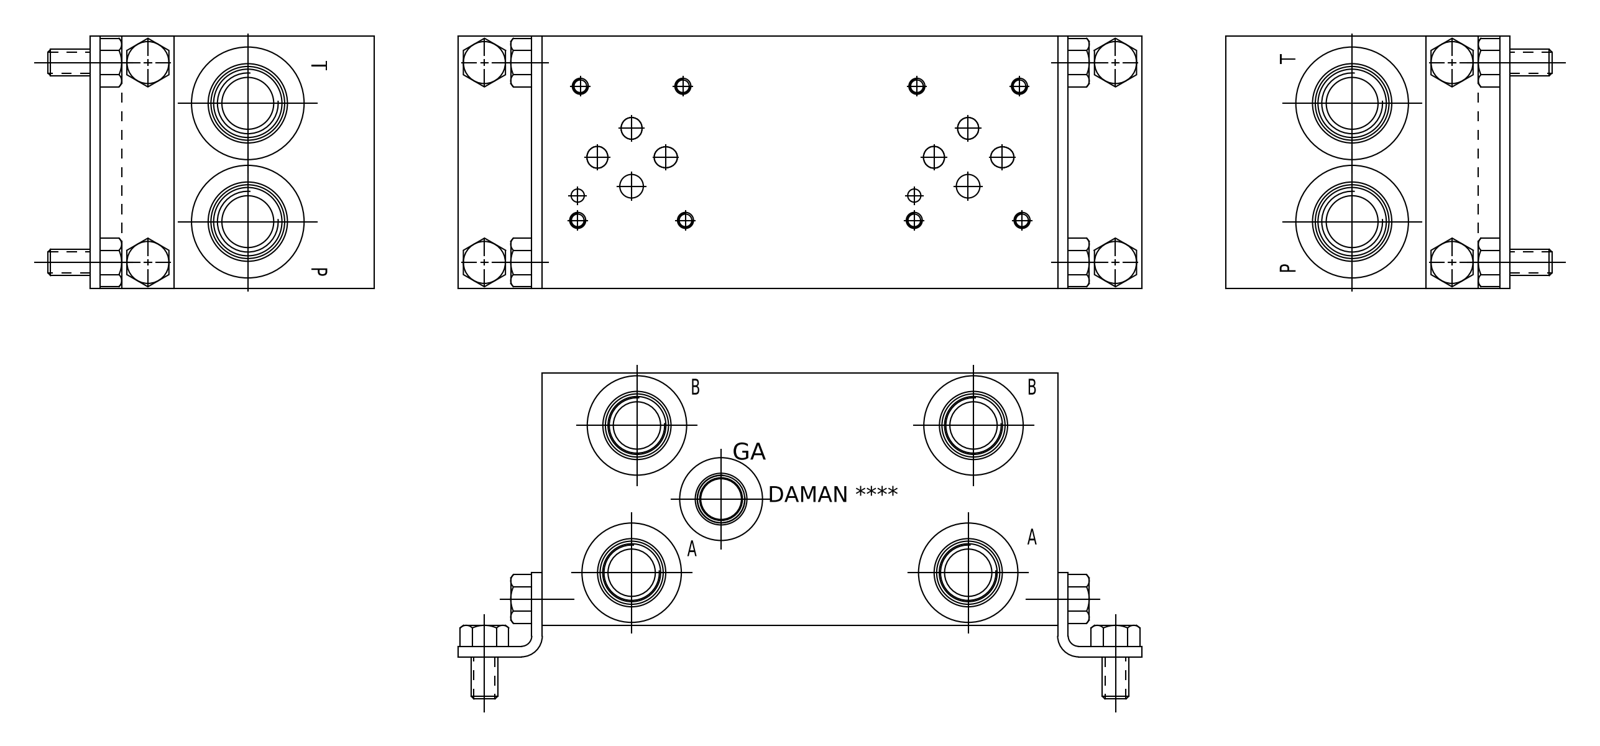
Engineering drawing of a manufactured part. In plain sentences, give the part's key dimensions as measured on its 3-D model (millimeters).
The part is named "Part_AD03S024S_3D". Its 3-D file was written by "Autodesk Inventor 2019 (AUTOMOTIVE_DESIGN)". It is 1 solid with 658 faces: 355 planar, 82 cylindrical and 221 other. Overall it measures 155.57 by 76.2 by 76.2 millimeters. Its volume is 827 016 cubic millimeters and its surface area 77 389 square millimeters. Round holes: 8 of diameter 3.78, 8 of diameter 4.83, 5 of diameter 14.27, 4 of diameter 6.35, 4 of diameter 17.5, 4 of diameter 19.05, 4 of diameter 19.25, 4 of diameter 30.63, 2 of diameter 3.96, 2 of diameter 5.56, 2 of diameter 6.53, 2 of diameter 7.14. The main face-to-face distances are 76.2, 155.57, 0.79, 75.41, 154.78, 154.79, 154, 0.78, 16.66, 137.34. The hole center spacings are 101.6, 22.05, 33.55, 33.91, 40.5, 51.45, 7.5, 12.99.
